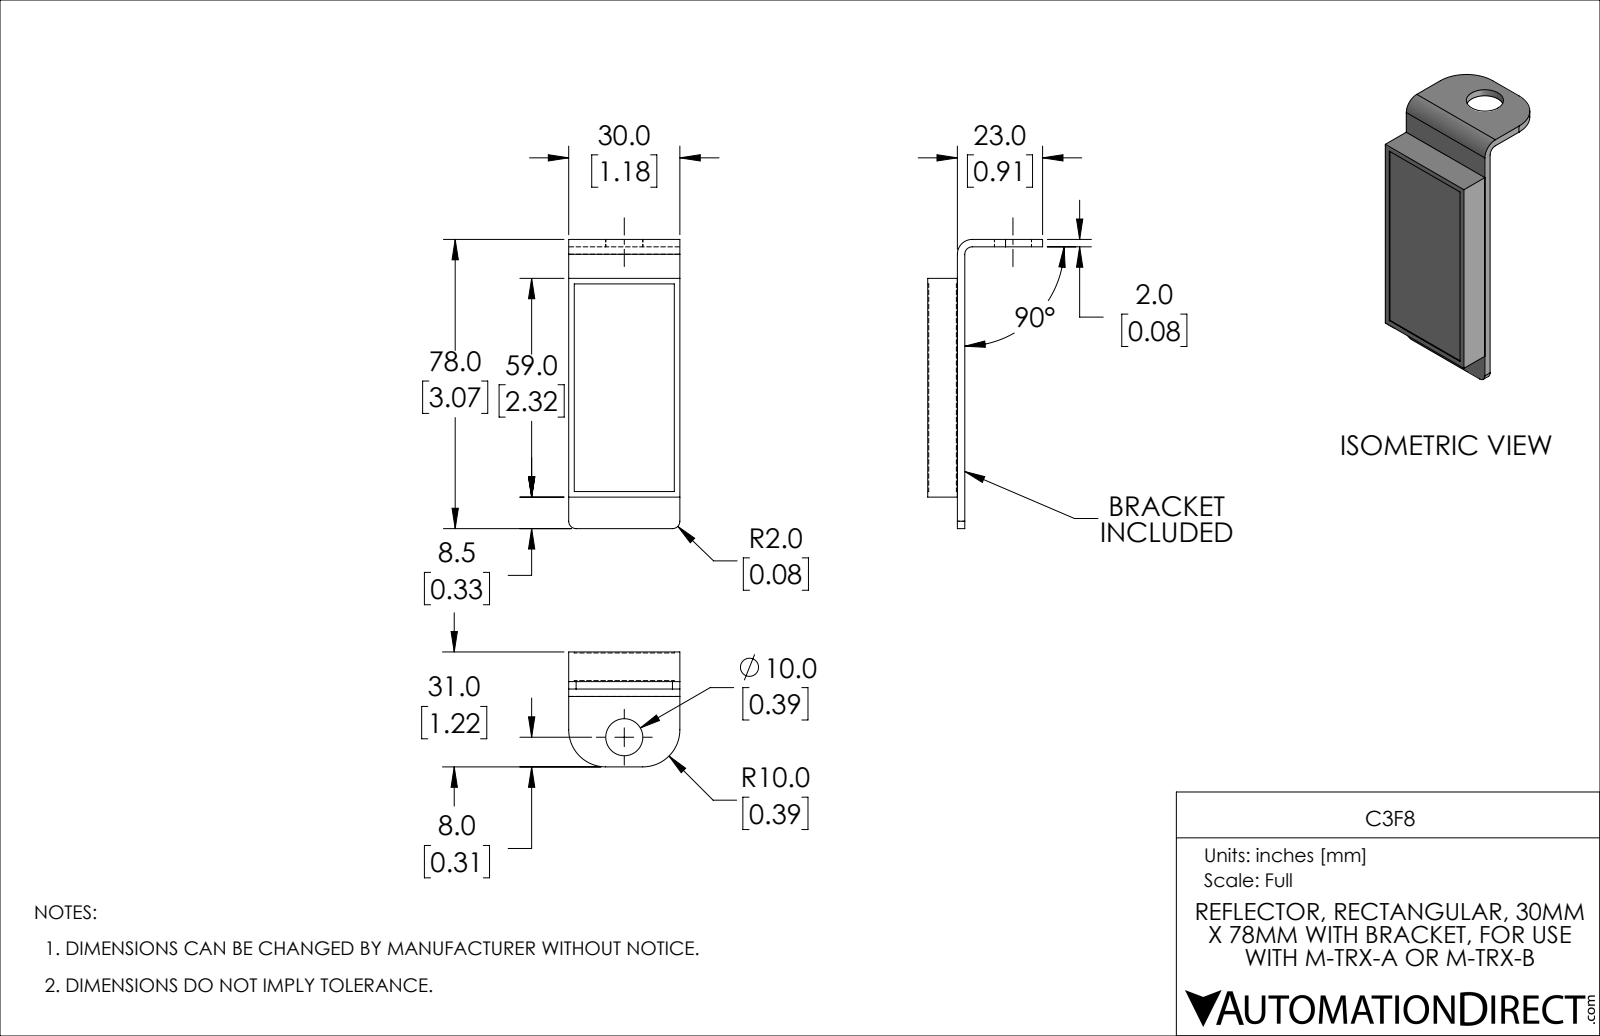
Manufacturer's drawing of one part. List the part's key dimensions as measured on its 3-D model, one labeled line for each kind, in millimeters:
Part name (STEP PRODUCT): BRACKET; C3F8
STEP written by: SolidWorks 2019 (AUTOMOTIVE_DESIGN)
Units: millimetres
Bodies: 2 solids, 31 faces (24 planar, 7 cylindrical, 0 other)
Overall size (bounding box): 78 × 31 × 30
Volume: 18 969 mm³ · Surface area: 11 222 mm²
Round holes (diameter × count): ⌀10 ×1
Partial cylindrical surfaces — rounded edges, fillets, slot ends (radius × count): R2 ×3, R10 ×2, R4 ×1
Main face-to-face distances: 2, 7.73, 2.27, 9.73, 7.46, 30, 8.5, 67.5, 10, 8
